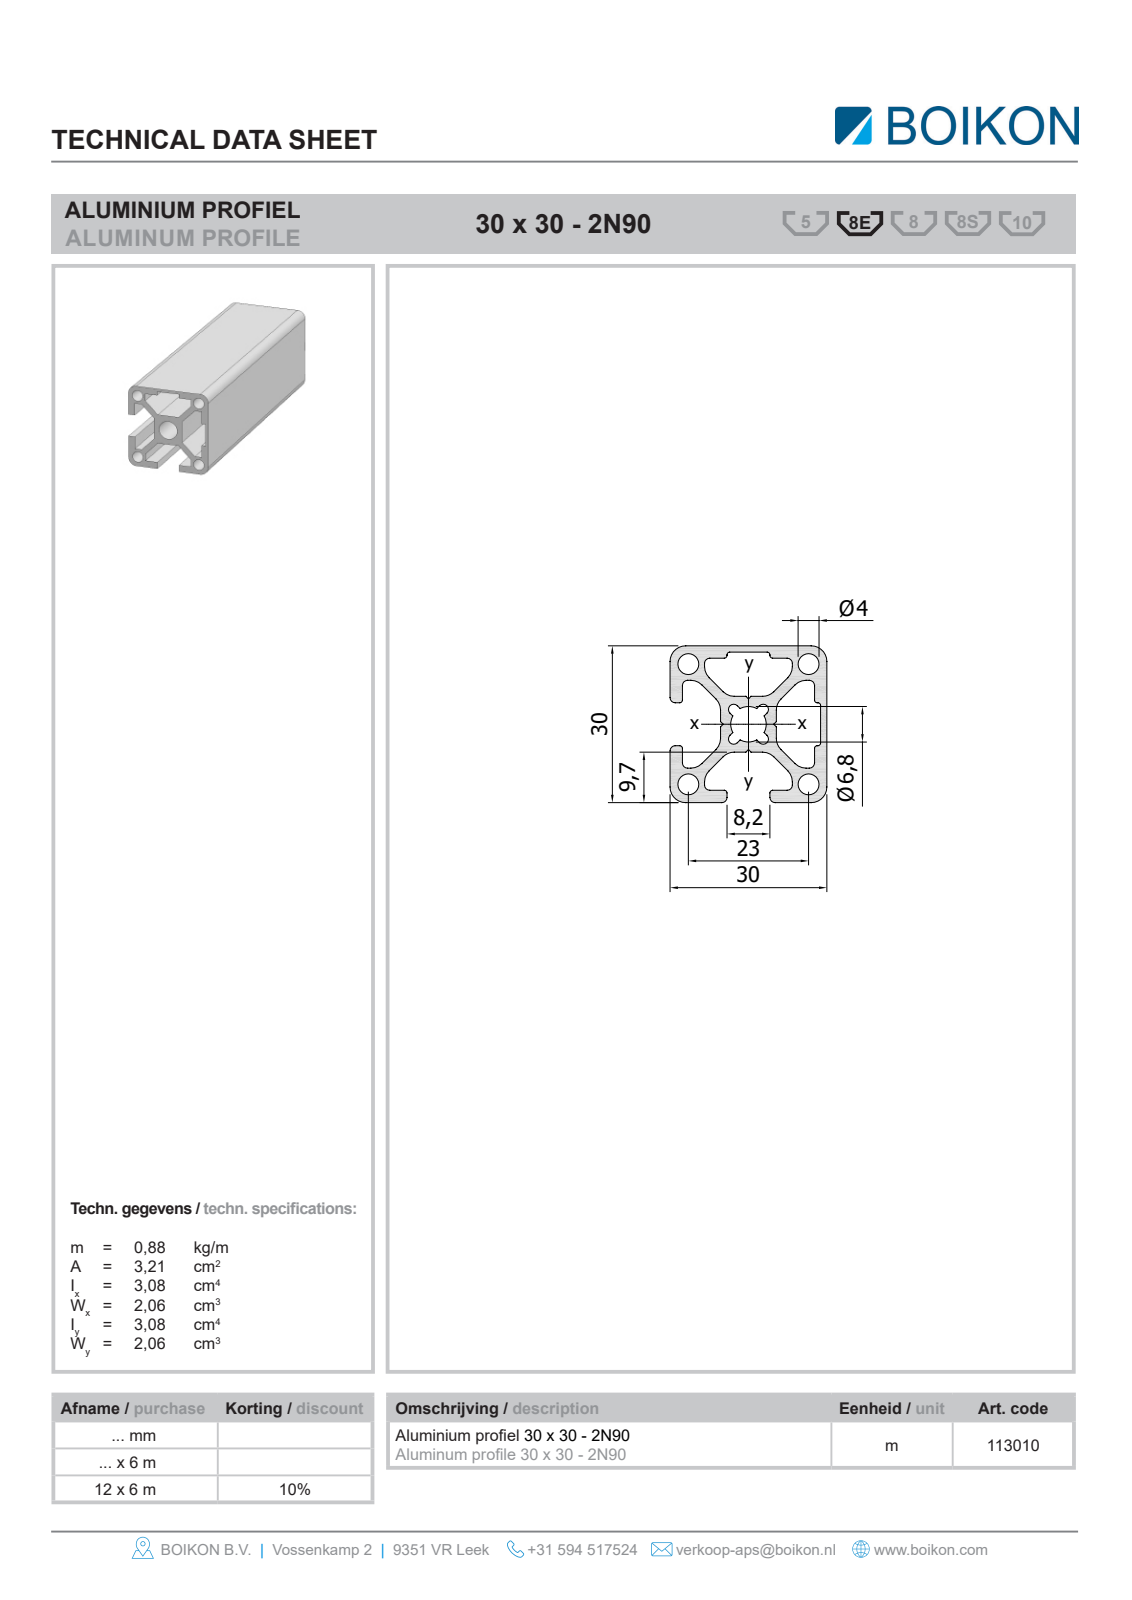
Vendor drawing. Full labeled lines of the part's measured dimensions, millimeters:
Part name (STEP PRODUCT): Root; 11301030x30-2N90BOIKON0
STEP written by: HiCAD 2013 1802.4 Build 509 (AUTOMOTIVE_DESIGN)
Units: millimetres
Bodies: 1 solid, 55 faces (46 planar, 9 cylindrical, 0 other)
Overall size (bounding box): 1000 × 30 × 30
Volume: 330 027 mm³ · Surface area: 343 446 mm²
Round holes (diameter × count): ⌀4 ×4, ⌀6.8 ×1
Partial cylindrical surfaces — rounded edges, fillets, slot ends (radius × count): R3 ×4
Main face-to-face distances: 2.4, 27.6, 30, 9.7, 20.3, 7.3, 17.9, 2, 6.4, 23.6
Hole centre spacings: 16.26, 23, 32.53
